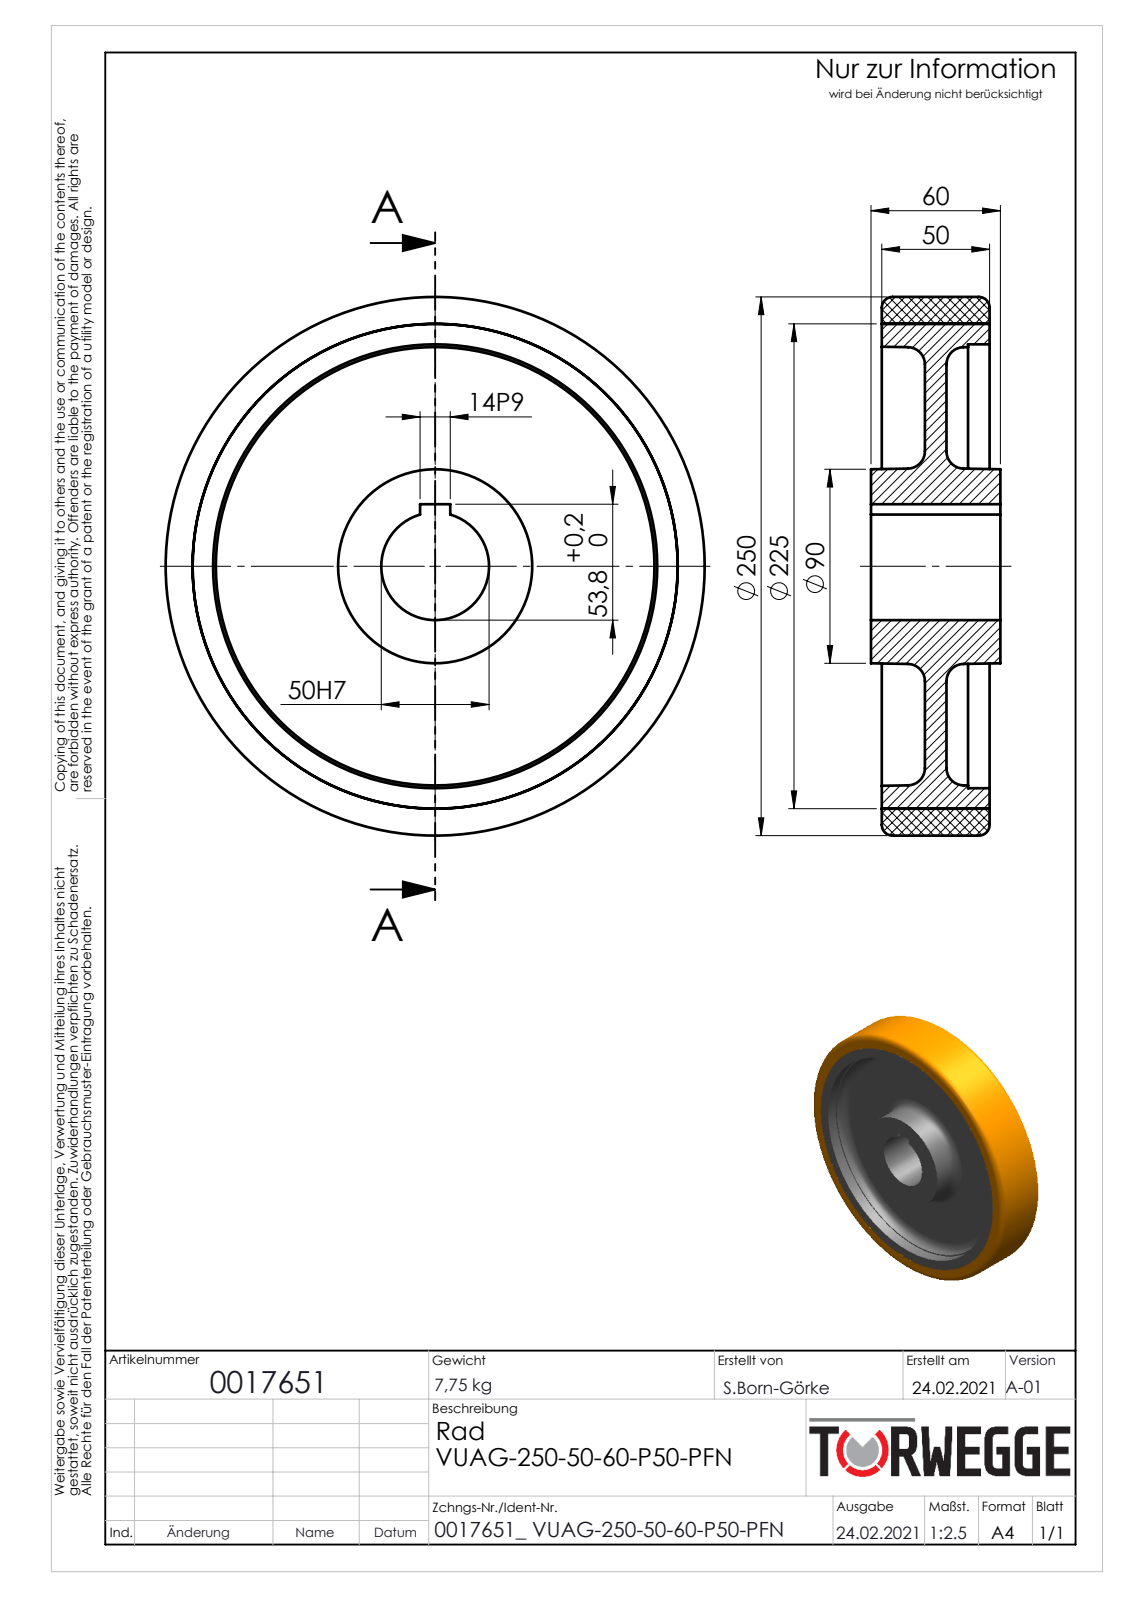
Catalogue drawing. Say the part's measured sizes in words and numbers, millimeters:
The part is named "0017651". Its 3-D file was written by "SolidWorks 2020 (AUTOMOTIVE_DESIGN)". It is 2 solids with 43 faces: 12 planar, 11 cylindrical and 20 other. Overall it measures 250 by 250 by 60 millimeters. Its volume is 1 363 000 cubic millimeters and its surface area 243 883 square millimeters. Round holes: 1 of diameter 50, 1 of diameter 206, 1 of diameter 225. Round bosses or shafts: 1 of diameter 250. The main face-to-face distances are 20, 30, 10, 50, 5, 25, 35, 55, 60, 15.
